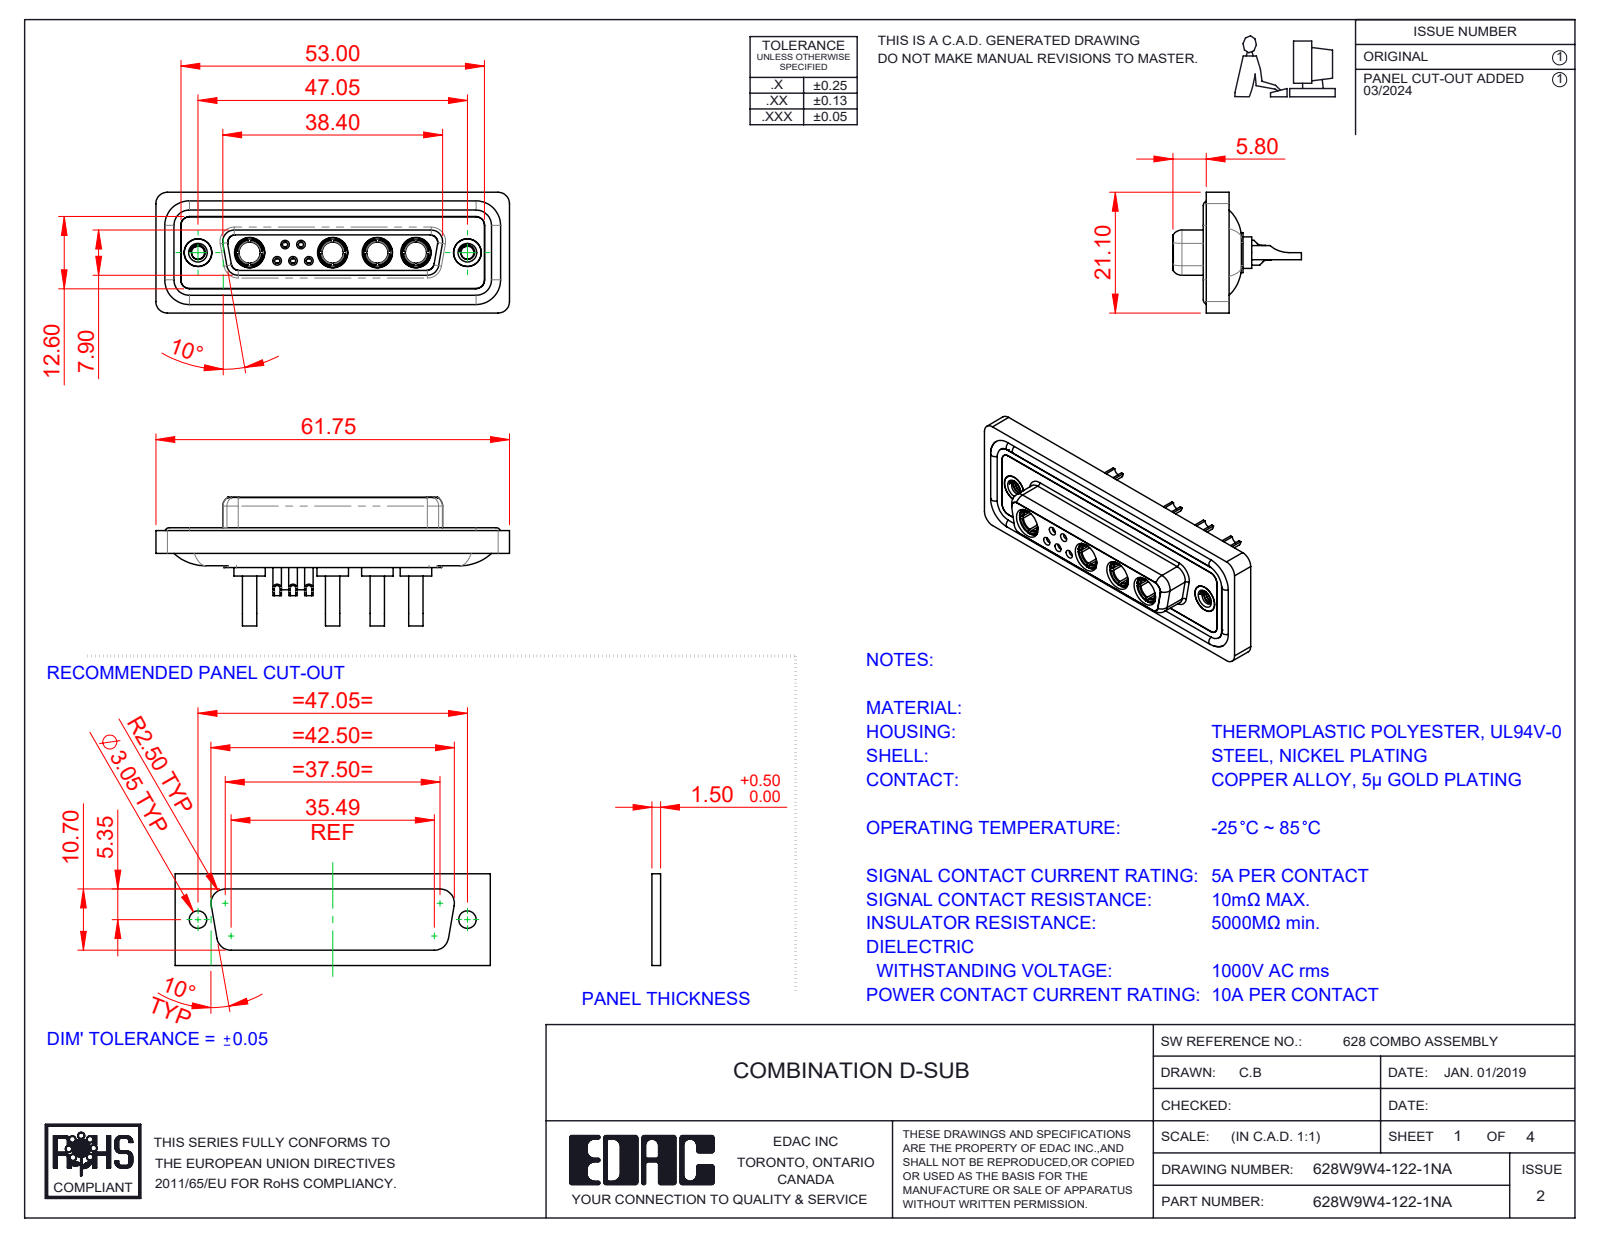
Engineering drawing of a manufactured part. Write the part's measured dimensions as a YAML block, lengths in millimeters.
part_name: "628Combo Contact Row 1_22; 628Combo Waterproof Housing_25 Contacts; 628W9W4-122-1NA; 628Combo Threaded Rivet_A (+5 more)"
step_written_by: "SolidWorks 2023 (CONFIG_CONTROL_DESIGN)"
units: millimeters
bodies: {solids: 20, faces: 975, planar: 314, cylindrical: 399, other: 262}
overall_size: [61.75, 22.45, 21.1]
volume: 8225
surface_area: 13805
round_holes:
  - {diameter: 4.85, count: 6}
  - {diameter: 0.9, count: 5}
  - {diameter: 1, count: 5}
  - {diameter: 1.1, count: 5}
  - {diameter: 1.5, count: 5}
  - {diameter: 2, count: 5}
  - {diameter: 1.7, count: 4}
  - {diameter: 3.7, count: 4}
  - {diameter: 5.3, count: 4}
  - {diameter: 1.6, count: 3}
  - {diameter: 1.7, count: 2}
  - {diameter: 2.26, count: 2}
round_bosses_or_shafts:
  - {diameter: 1.6, count: 6}
  - {diameter: 2.2, count: 5}
  - {diameter: 5.5, count: 4}
  - {diameter: 5.2, count: 4}
  - {diameter: 4.96, count: 4}
  - {diameter: 4.75, count: 4}
  - {diameter: 3.75, count: 4}
  - {diameter: 2.5, count: 4}
partial_cylinders:
  - {radius: 1.5, count: 22}
  - {radius: 2, count: 18}
  - {radius: 1.35, count: 8}
  - {radius: 1.6, count: 8}
  - {radius: 1, count: 6}
  - {radius: 0.25, count: 4}
  - {radius: 0.5, count: 4}
  - {radius: 0.6, count: 4}
face_to_face_distances: [0.4, 1.8, 7.45, 5.65, 0.5, 7.05, 6.6, 1.6, 1.1, 2.9]
hole_center_spacings: [3.16, 2.77, 5.03, 2.76, 4.4, 5.02, 5.54, 5.73]
